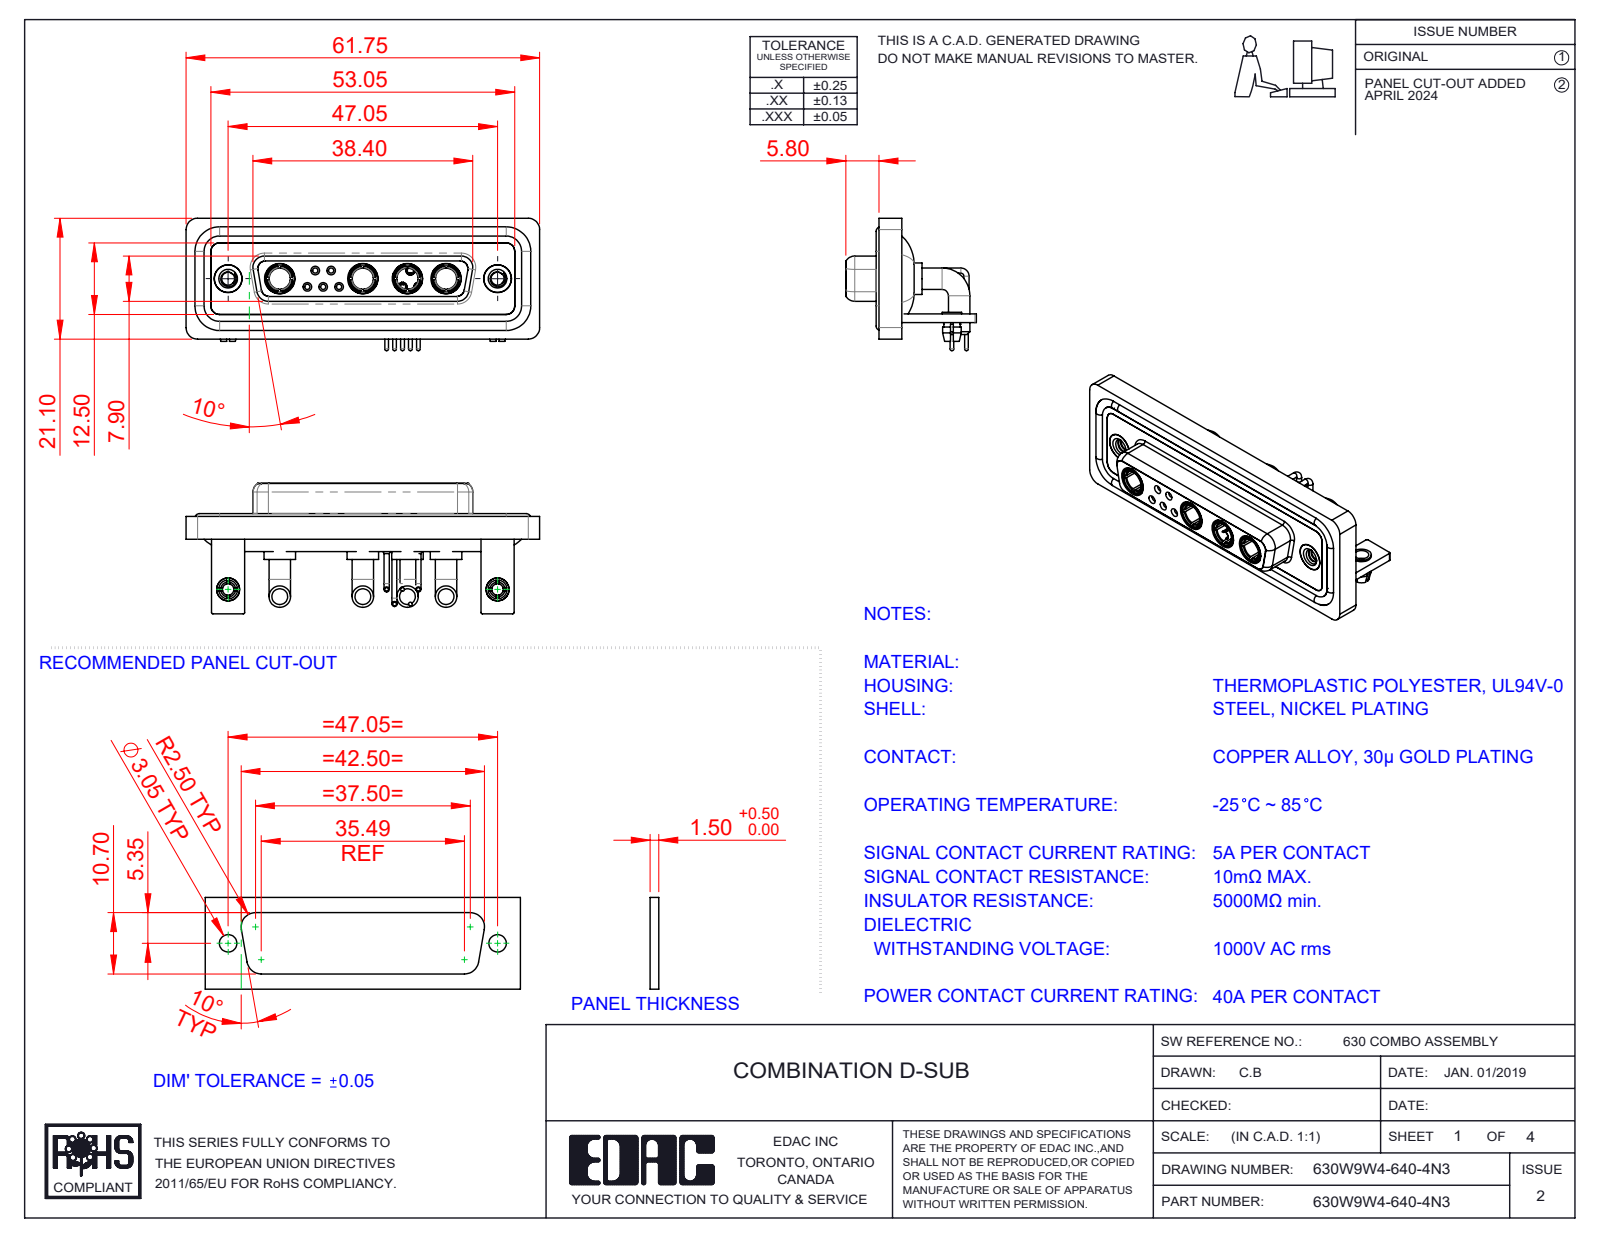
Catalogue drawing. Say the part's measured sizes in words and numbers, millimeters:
The part is named "630Combo Shell Front_25 Contacts; 630Combo Housing_9W4; 630Combo Contact Row 1_50 Contacts; 630Combo Threaded Rivet_2 (+7 more)". Its 3-D file was written by "SolidWorks 2023 (CONFIG_CONTROL_DESIGN)". It is 24 solids with 1103 faces: 364 planar, 459 cylindrical and 280 other. Overall it measures 61.75 by 23.12 by 22.8 millimeters. Its volume is 9 145 cubic millimeters and its surface area 15 168 square millimeters. Round holes: 7 of diameter 2, 6 of diameter 4.85, 5 of diameter 0.9, 5 of diameter 1.1, 5 of diameter 1.5, 4 of diameter 3.7, 4 of diameter 5.3, 3 of diameter 1.6, 2 of diameter 1.7, 2 of diameter 2.26, 2 of diameter 2.5, 2 of diameter 3.2. Round bosses or shafts: 10 of diameter 0.9, 9 of diameter 1.6, 8 of diameter 3.75, 5 of diameter 2, 5 of diameter 1.5, 5 of diameter 0.65, 4 of diameter 5.5, 4 of diameter 5.2. Partial cylindrical surfaces (rounded edges, fillets, slot ends): 19 of radius 2, 18 of radius 1.5, 16 of radius 0.25, 8 of radius 1.35, 8 of radius 1.6, 5 of radius 0.5, 4 of radius 0.6, 4 of radius 0.65. The main face-to-face distances are 0.4, 1.8, 2.9, 3.7, 1.5, 4.1, 1.1, 1.4, 1.6, 2.5. The hole center spacings are 3.16, 2.77, 5.04, 13.85, 11.08, 12.79, 15.5, 5.54.
